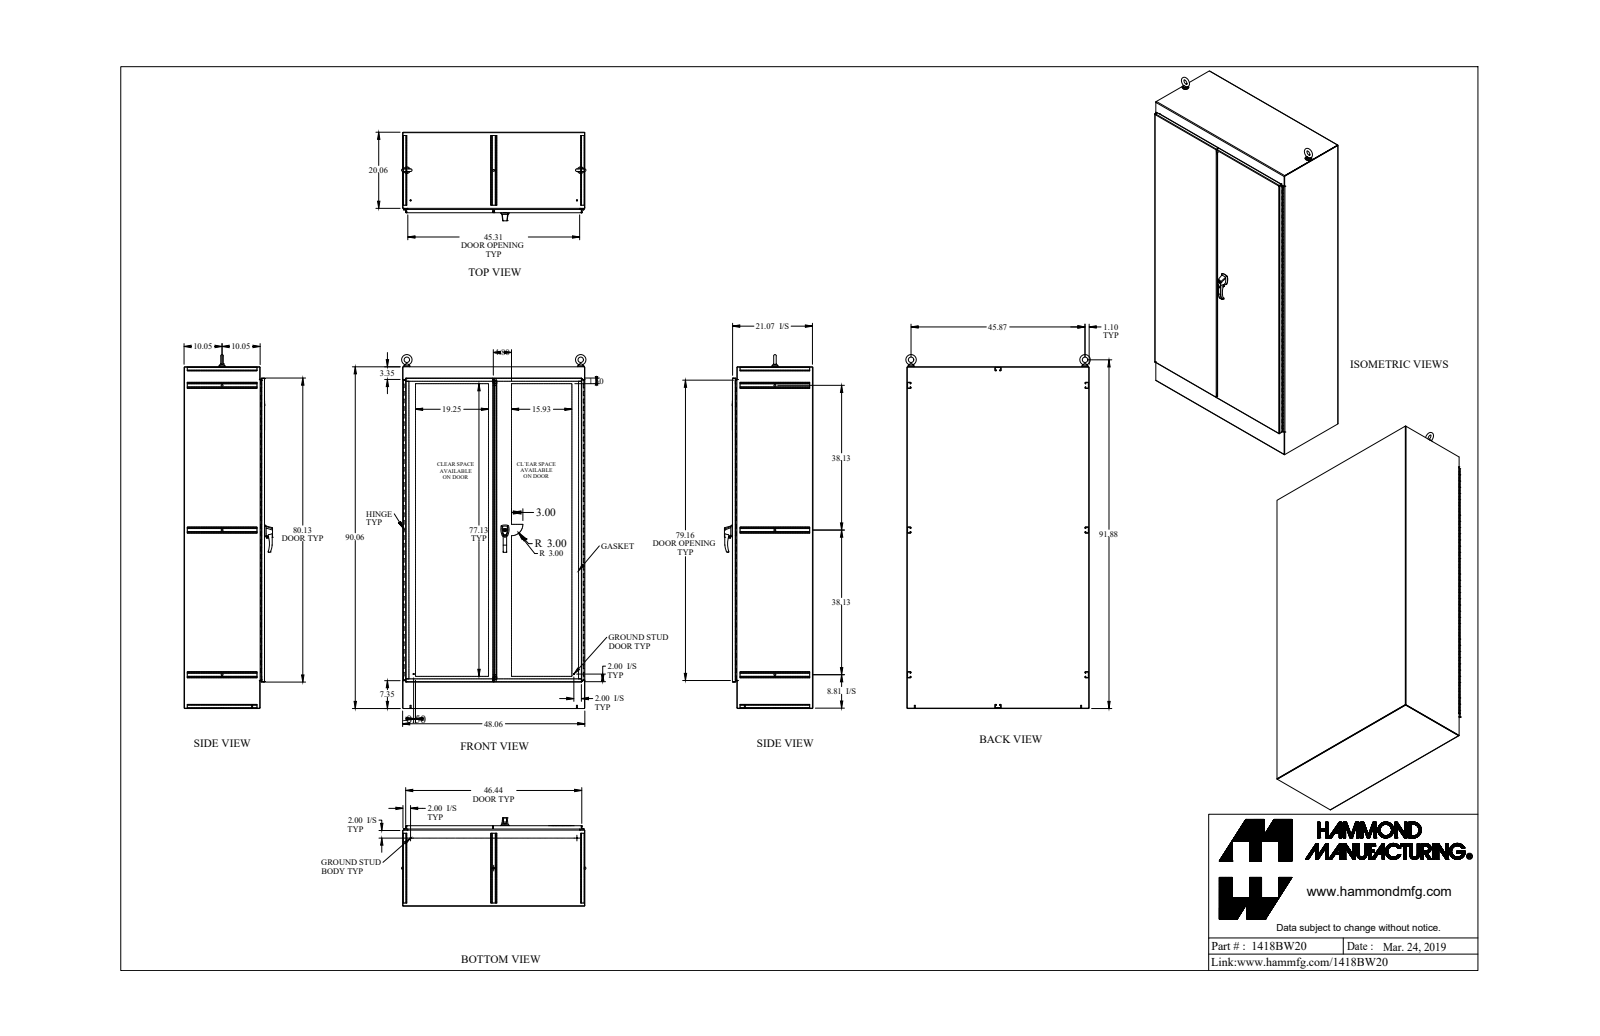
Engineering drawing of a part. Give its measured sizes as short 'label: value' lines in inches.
name: 1418BW20
written by: SolidWorks 2019 (AUTOMOTIVE_DESIGN)
unit: in
bodies: 74 solids, 3305 faces (1910 planar, 1256 cylindrical, 139 other)
size: 93.713 × 49.118 × 23.337
volume: 1 682 in³; area: 34 398 in²
holes: 28× ⌀0.304, 7× ⌀0.35, 4× ⌀0.5, 3× ⌀0.25, 2× ⌀0.11, 2× ⌀0.257, 2× ⌀0.28, 2× ⌀0.281, 2× ⌀0.313, 2× ⌀0.39, 2× ⌀0.413, 2× ⌀0.527
bosses: 6× ⌀0.281, 4× ⌀0.25, 2× ⌀1.75, 2× ⌀1.5, 2× ⌀1.25, 2× ⌀1, 2× ⌀0.75, 2× ⌀0.738
rounds: 54× R0.043, 48× R0.138, 25× R0.5, 22× R0.125, 16× R0.018, 15× R0.06, 8× R0.048, 8× R0.05
face distances: 0.095, 0.125, 0.072, 21.096, 21.222, 21.024, 21.15, 47.965, 47.87, 89.965
hole spacings: 6, 46.715, 12, 47.857, 18, 49.702, 24, 52.176
